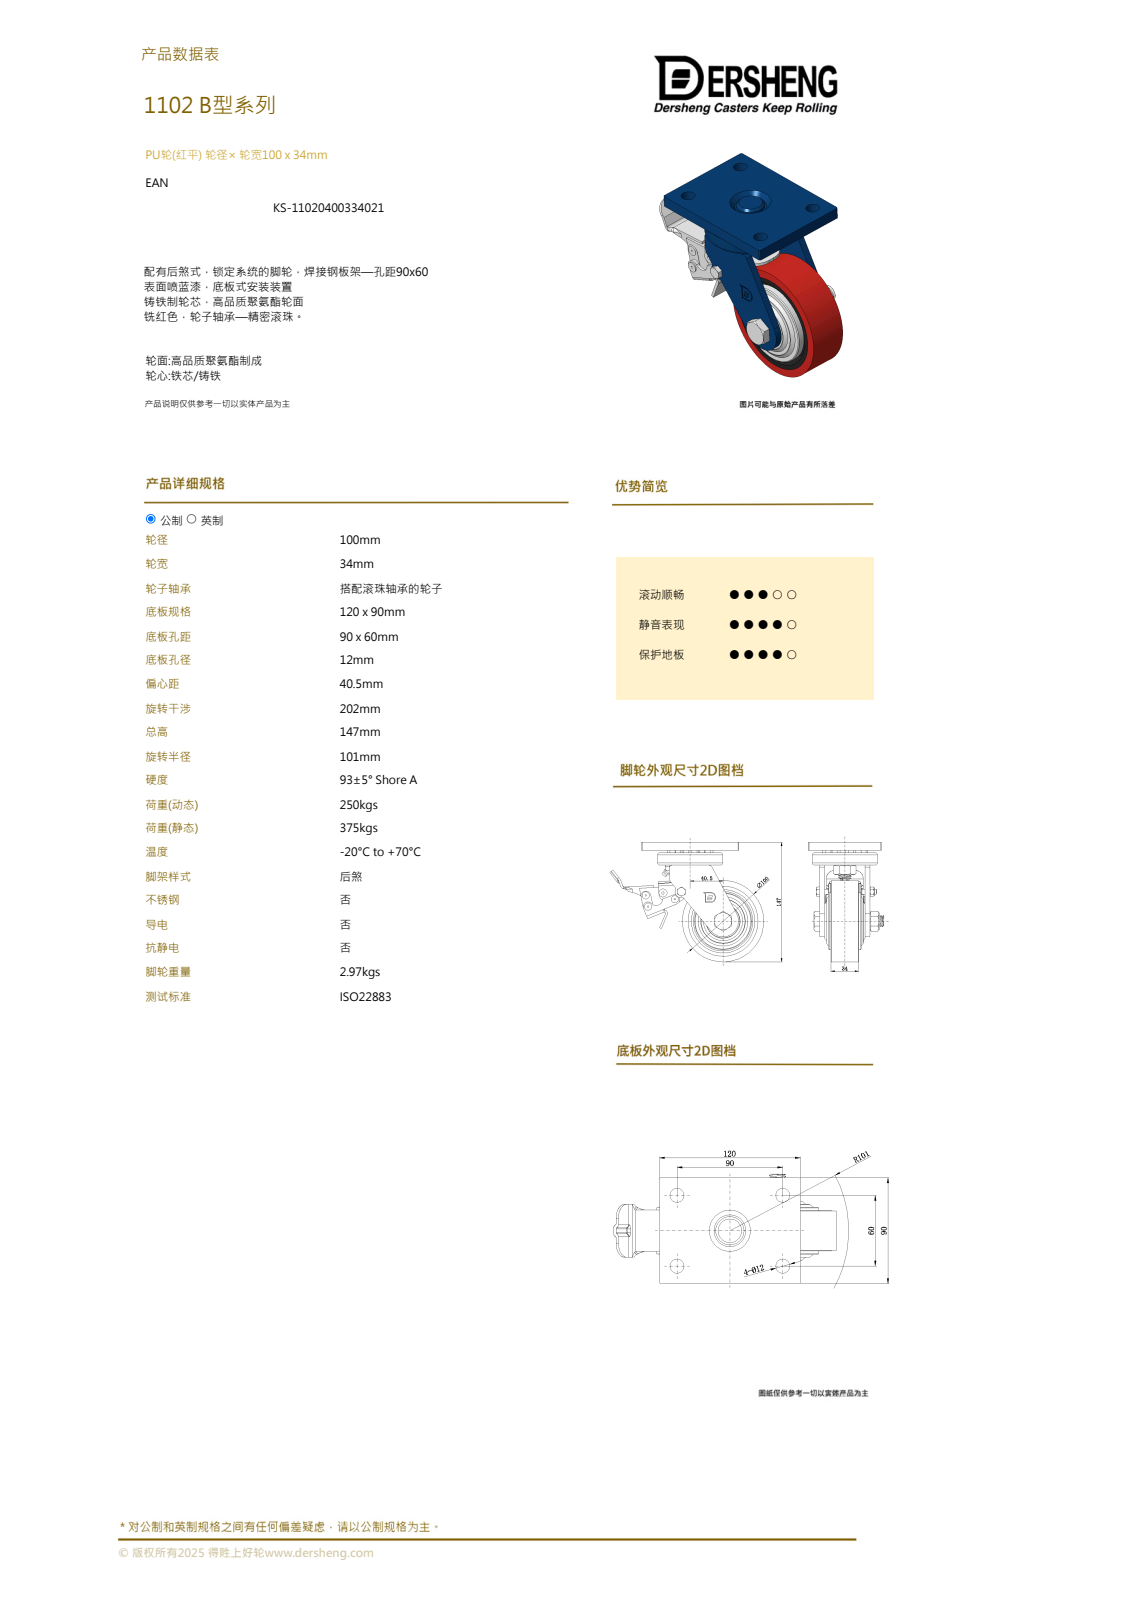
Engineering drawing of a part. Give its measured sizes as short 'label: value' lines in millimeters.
written by: CREO PARAMETRIC BY PTC INC, 2022484 (CONFIG_CONTROL_DESIGN)
unit: mm
bodies: 0 solids, 611 faces (197 planar, 200 cylindrical, 214 other)
size: 189.3 × 147 × 93
holes: 4× ⌀12, 2× ⌀30, 1× ⌀31, 1× ⌀68.6
bosses: 5× ⌀1, 3× ⌀9, 3× ⌀5, 2× ⌀20, 2× ⌀8, 2× ⌀6, 1× ⌀100, 1× ⌀80
rounds: 14× R3, 7× R1, 5× R0.5, 4× R6, 3× R2.5, 3× R3.5, 3× R4, 3× R12
face distances: 10, 6, 56, 2.5, 14, 18, 62, 5, 28, 15
hole spacings: 54.08, 60, 90, 108.17
